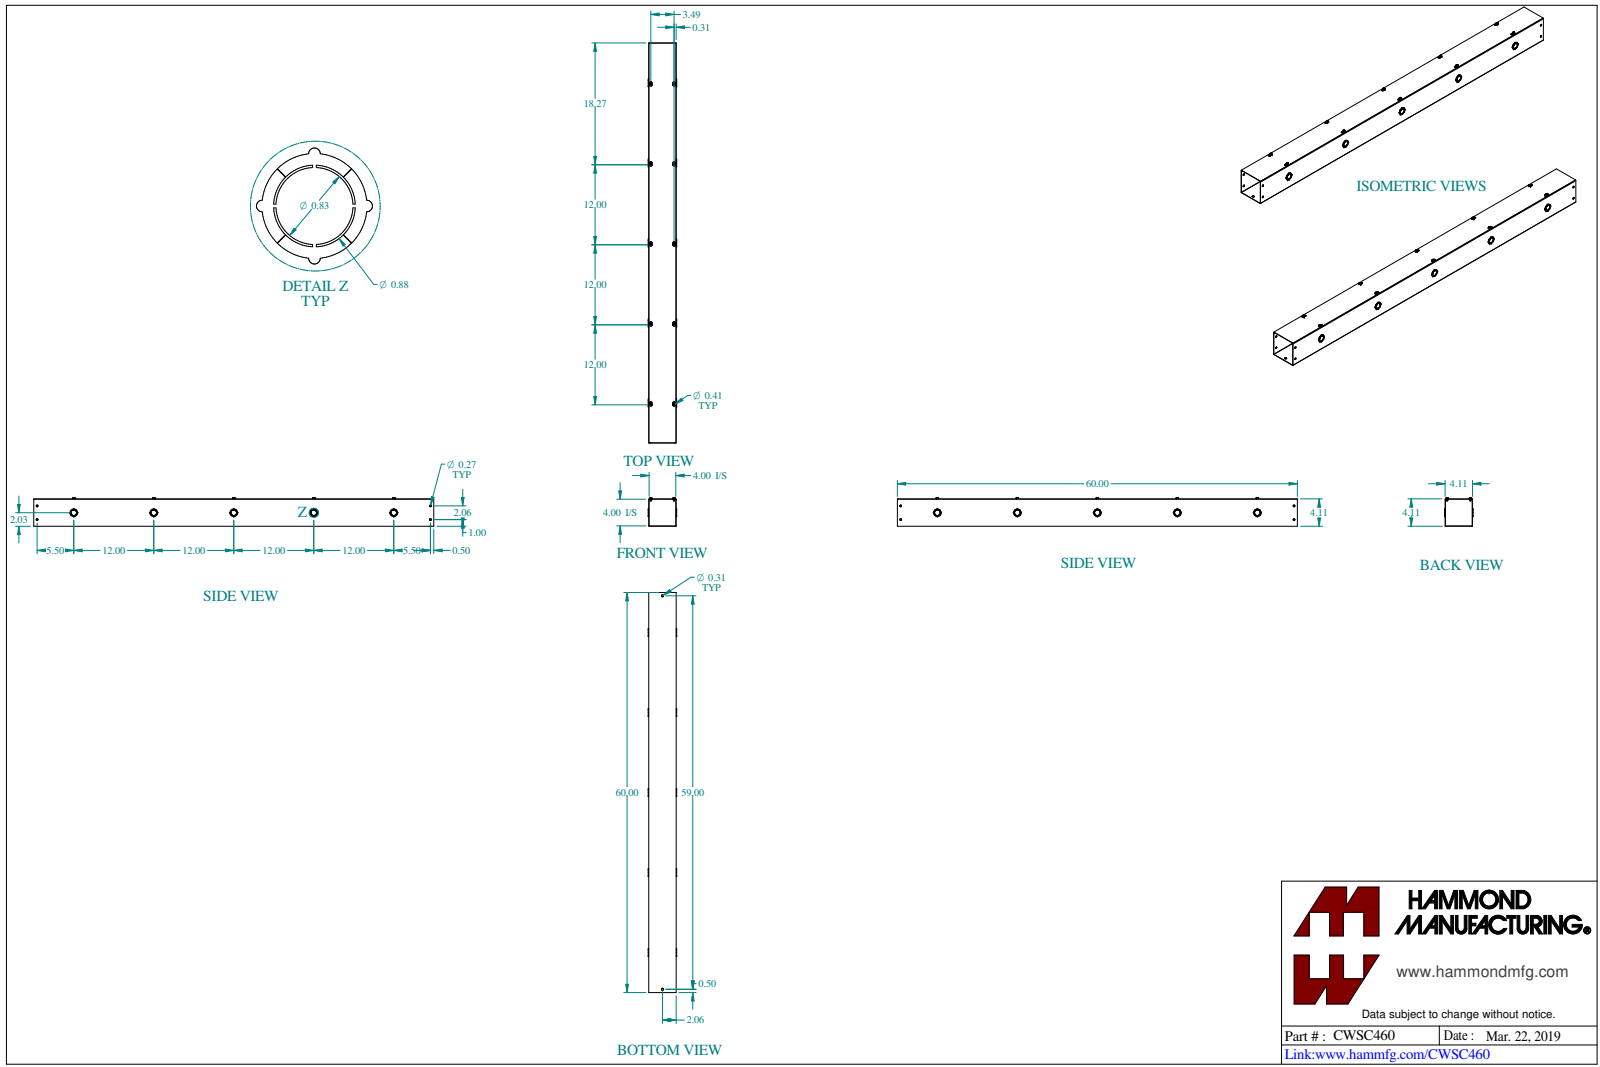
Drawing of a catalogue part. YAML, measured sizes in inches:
part_name: "CWSC460"
step_written_by: "SolidWorks 2023 (CONFIG_CONTROL_DESIGN)"
units: inches
bodies: {solids: 12, faces: 786, planar: 348, cylindrical: 378, other: 60}
overall_size: [60, 4.289, 4.258]
volume: 58.68
surface_area: 2057
round_holes:
  - {diameter: 0.177, count: 10}
  - {diameter: 0.875, count: 5}
  - {diameter: 0.266, count: 4}
  - {diameter: 0.313, count: 2}
round_bosses_or_shafts:
  - {diameter: 0.375, count: 10}
  - {diameter: 0.19, count: 10}
  - {diameter: 1.125, count: 5}
  - {diameter: 1.125, count: 5}
  - {diameter: 0.825, count: 5}
partial_cylinders:
  - {radius: 0.062, count: 15}
  - {radius: 0.125, count: 10}
  - {radius: 0.203, count: 10}
  - {radius: 0.063, count: 5}
  - {radius: 0.029, count: 4}
  - {radius: 0.086, count: 4}
face_to_face_distances: [0.057, 4.057, 4, 4.114, 3.943, 0.114, 0.072, 0.129, 4.129, 4.186]
hole_center_spacings: [12, 24, 12.497, 24.252, 36, 3.489, 5.595, 5.77]
